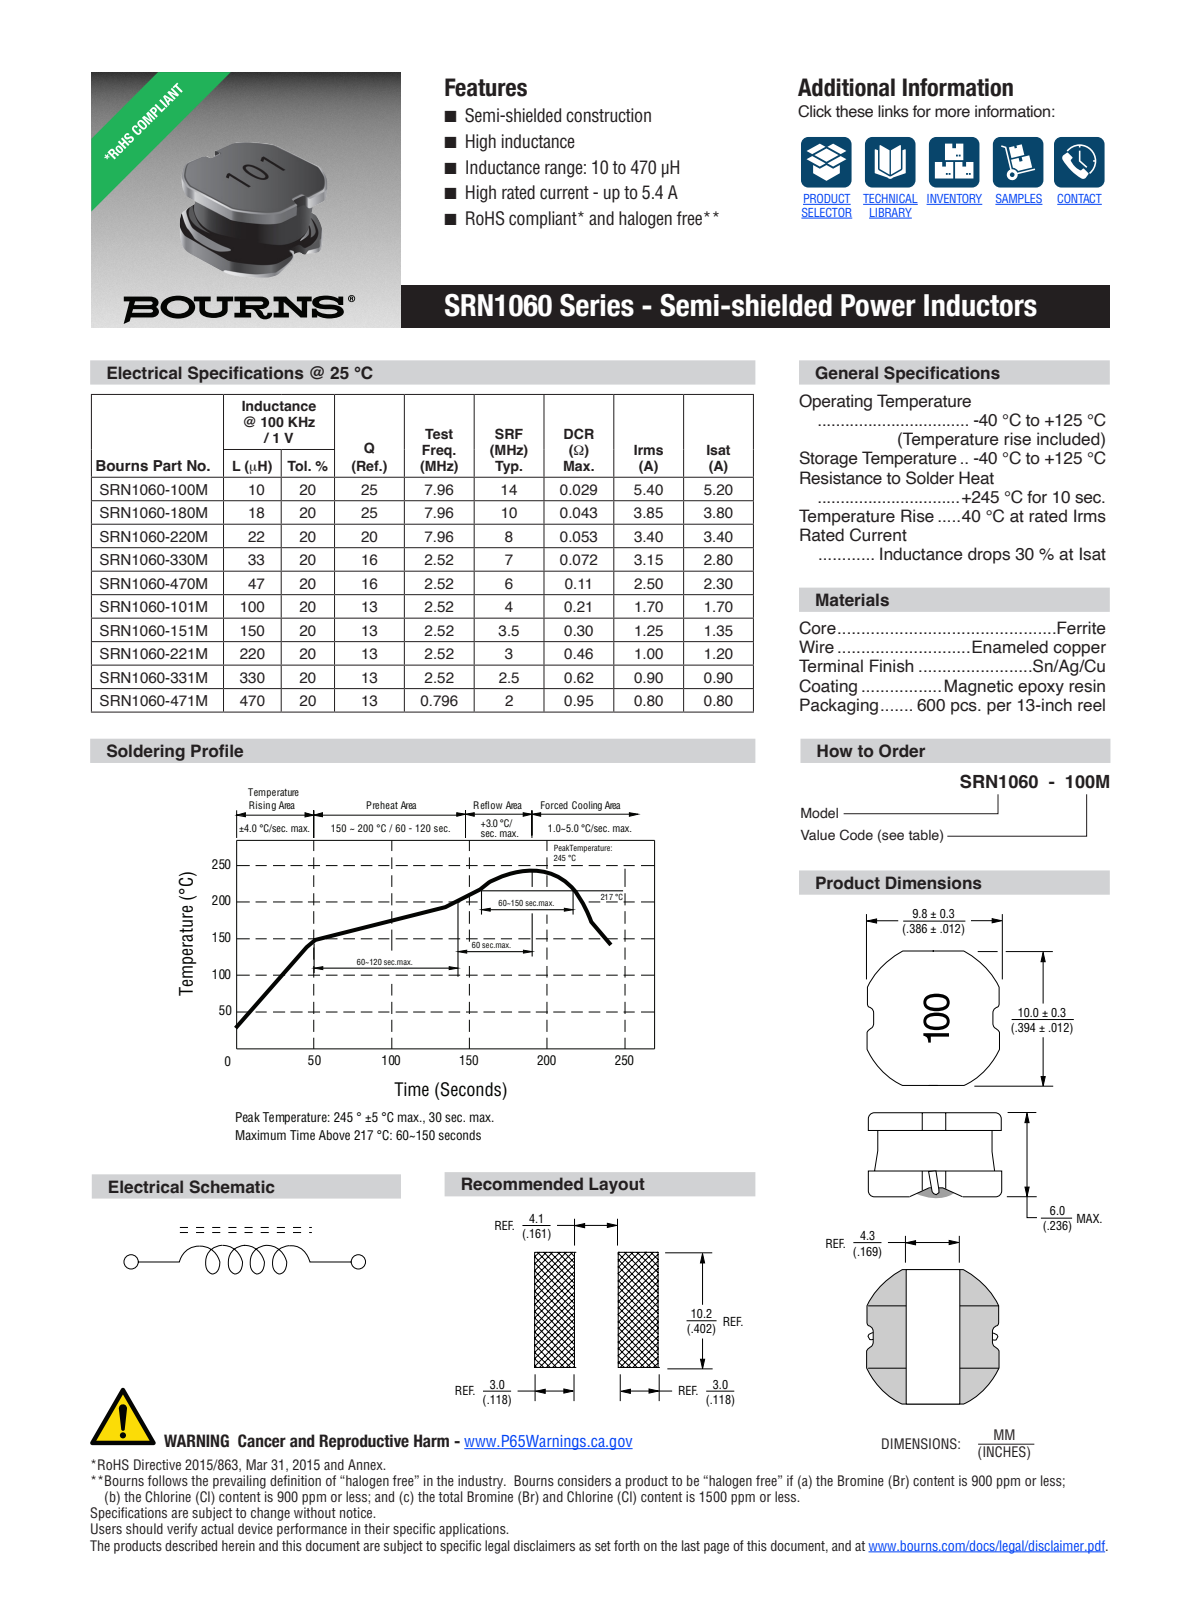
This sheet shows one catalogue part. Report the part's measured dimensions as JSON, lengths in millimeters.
{"part_name": "SRN1060", "step_written_by": "PRO/ENGINEER BY PARAMETRIC TECHNOLOGY CORPORATION, 2012230 (CONFIG_CONTROL_DESIGN)", "units": "millimeters", "bodies": {"solids": 1, "faces": 76, "planar": 26, "cylindrical": 34, "other": 16}, "overall_size": [10, 9.8, 6], "volume_mm3": 419, "surface_area_mm2": 409, "round_bosses_or_shafts": [[8.21, 1]], "partial_cylinders_radius": [[0.2, 6], [0.11, 4], [0.22, 4], [3.94, 4]], "face_to_face_distances": [6, 4, 2, 1.5, 2.5, 4.5, 5.25, 3.75, 1.25, 0.75]}
